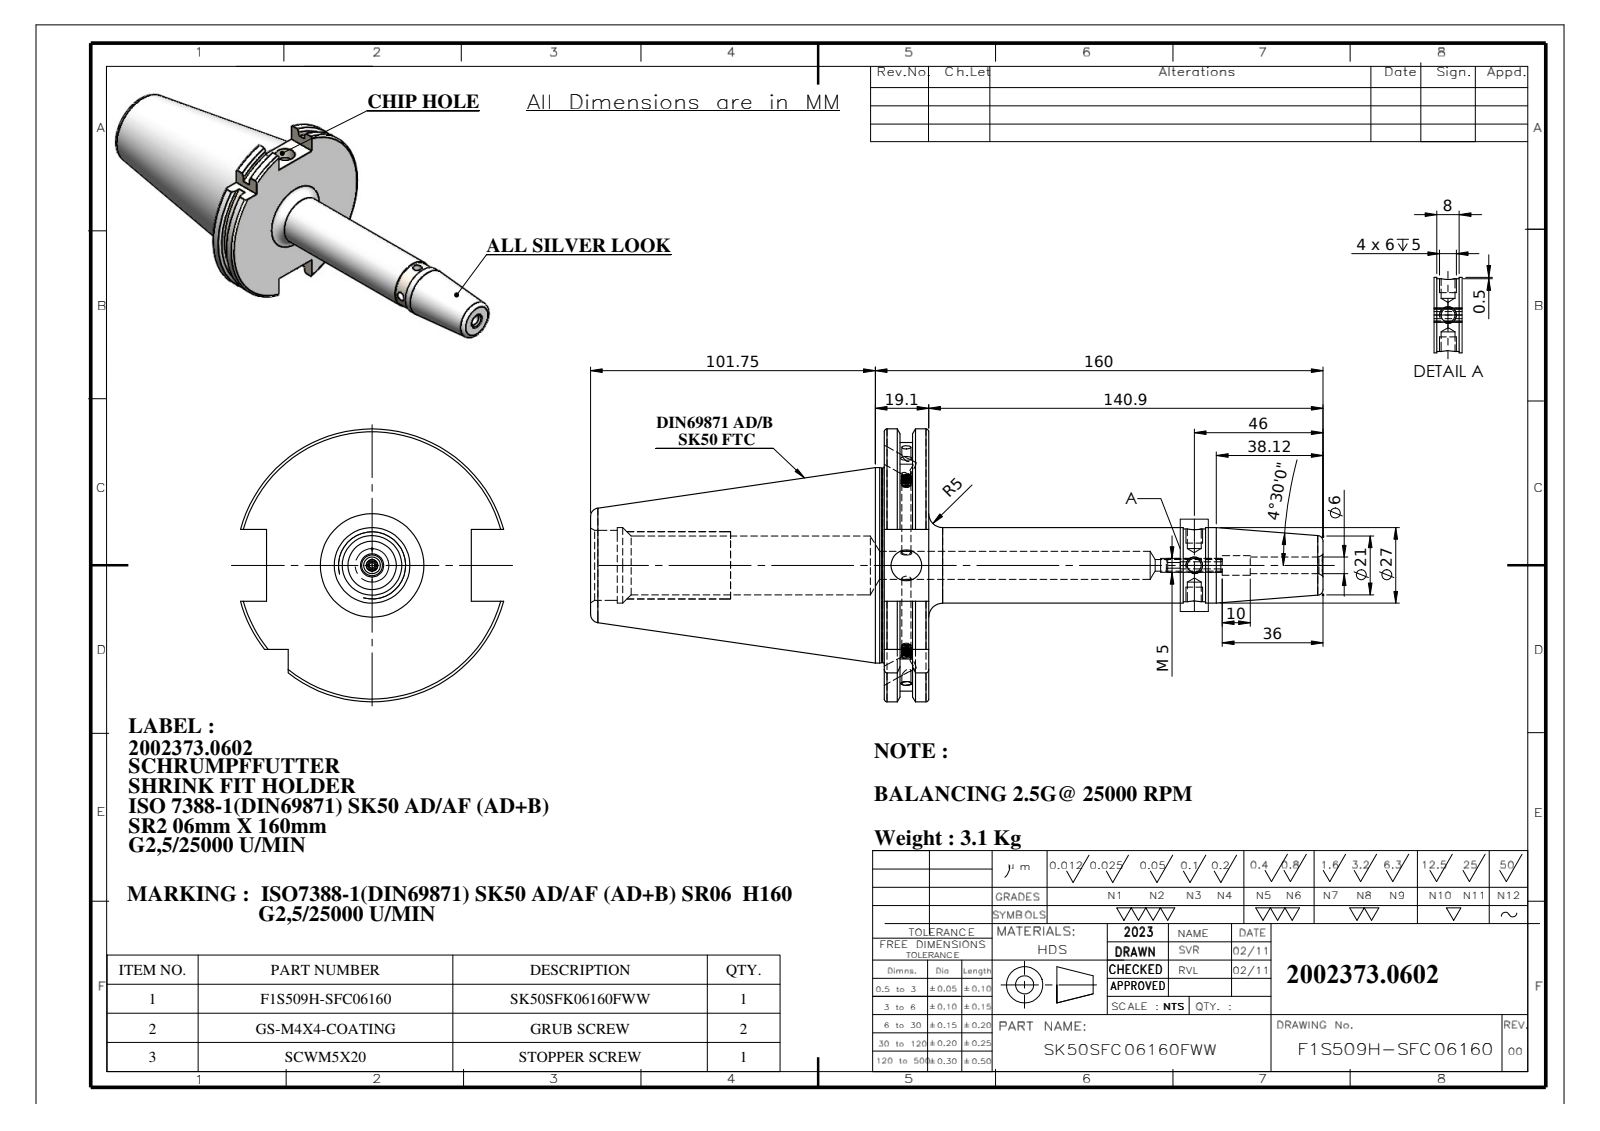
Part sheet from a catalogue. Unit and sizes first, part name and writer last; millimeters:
Units: millimetres
Overall size (bounding box): 261.75 × 97.5 × 94.05
Round holes (diameter × count): ⌀5 ×2, ⌀6 ×2, ⌀2 ×1, ⌀3.3 ×1, ⌀4 ×1, ⌀5.99 ×1, ⌀7 ×1, ⌀8 ×1, ⌀11 ×1, ⌀21 ×1, ⌀25 ×1, ⌀27 ×1
Round bosses / shafts (diameter × count): ⌀4 ×2, ⌀69.85 ×1, ⌀69.45 ×1, ⌀5 ×1
Partial cylindrical surfaces — rounded edges, fillets, slot ends (radius × count): R44.9 ×1, R48.75 ×1
Main face-to-face distances: 15.9, 5.66, 10.24, 10.14, 4.48, 5.76, 104.95, 110.61, 115.09, 120.85
Hole centre spacings: 102.9
Volume: 406 116 mm³ · Surface area: 58 509 mm²
Bodies: 4 solids, 181 faces (62 planar, 63 cylindrical, 56 other)
Part name (STEP PRODUCT): 91506-SR206160; socket set screw flat point_din_DIN 913 - M4 x 10-N; SCWM5X20; SK50SFC06160WW
STEP written by: SolidWorks 2018 (AUTOMOTIVE_DESIGN)
